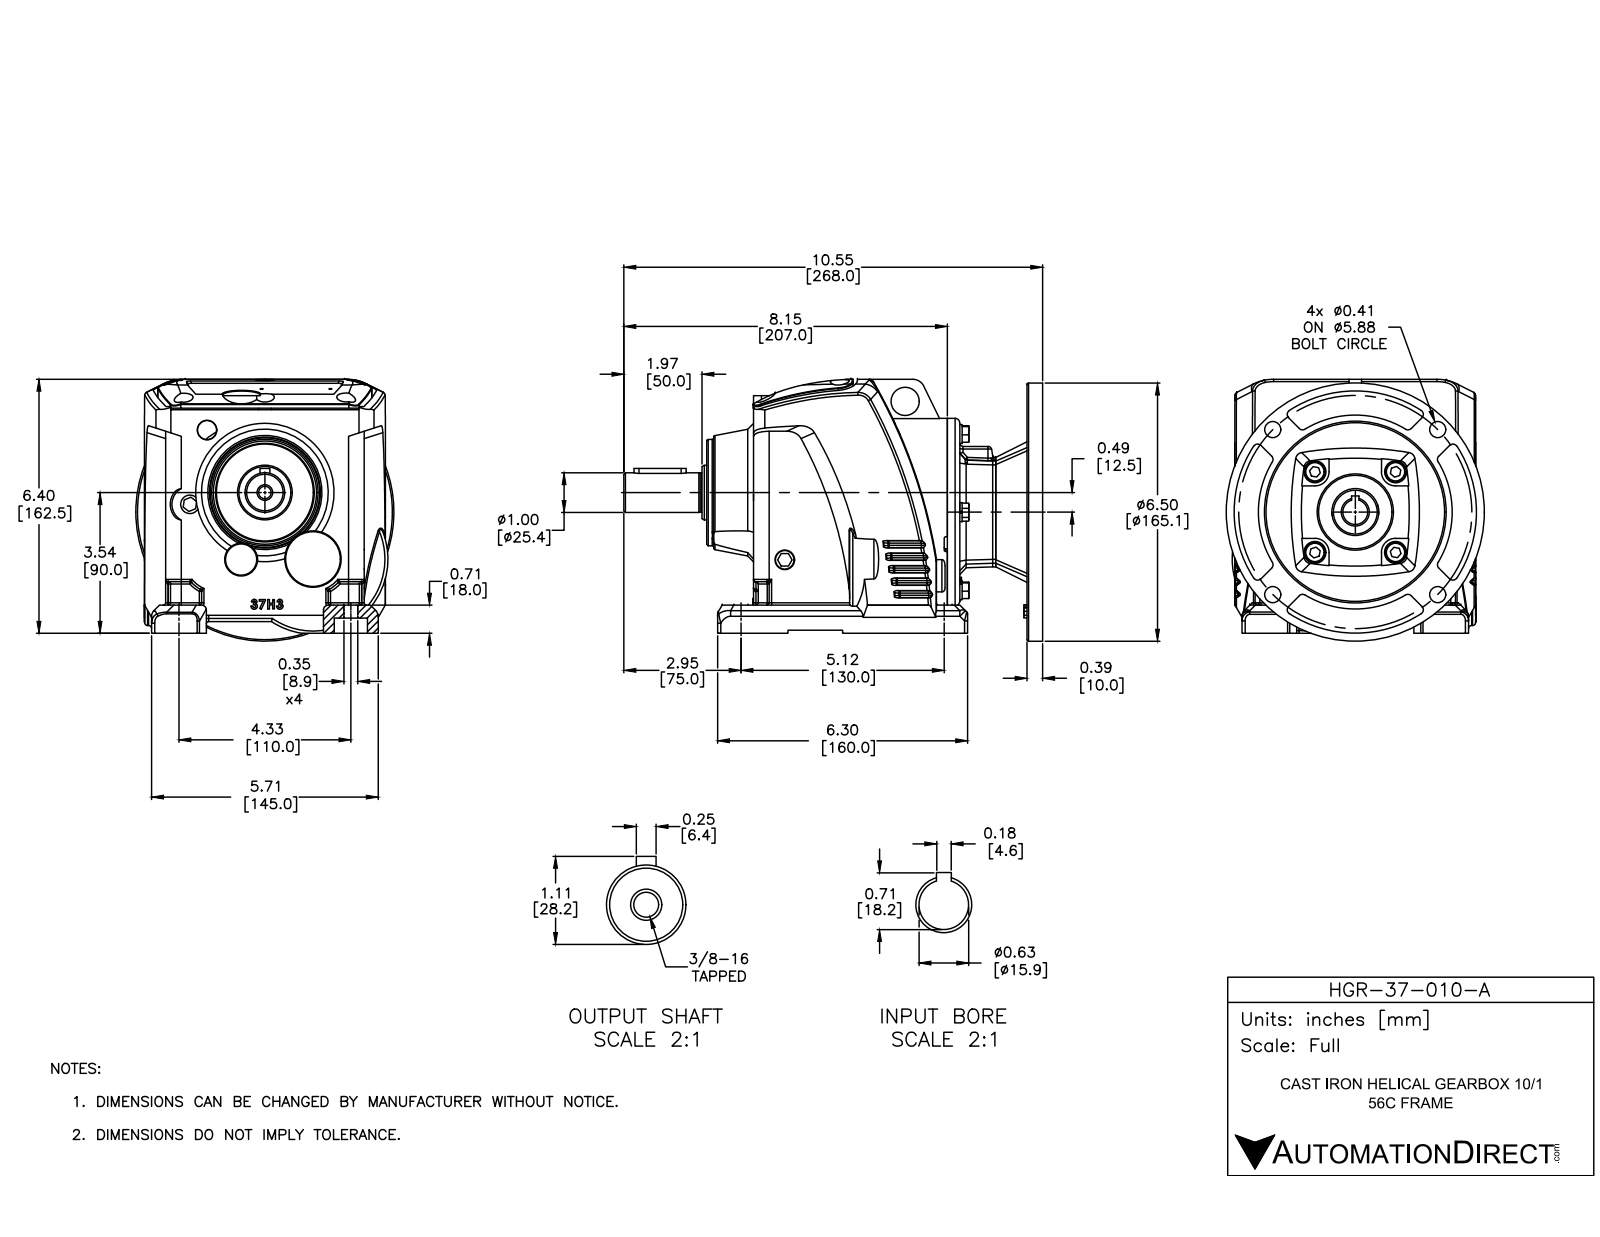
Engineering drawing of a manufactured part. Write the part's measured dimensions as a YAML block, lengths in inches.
part_name: "HGR-37-010-A"
step_written_by: "SolidWorks 2015 (AUTOMOTIVE_DESIGN)"
units: inches
bodies: {solids: 4, faces: 1036, planar: 343, cylindrical: 277, other: 416}
overall_size: [10.551, 6.596, 6.5]
volume: 169.7
surface_area: 383.8
round_holes:
  - {diameter: 0.472, count: 6}
  - {diameter: 0.406, count: 4}
  - {diameter: 0.55, count: 4}
  - {diameter: 0.276, count: 3}
  - {diameter: 0.079, count: 2}
  - {diameter: 0.354, count: 2}
  - {diameter: 0.394, count: 2}
  - {diameter: 0.313, count: 1}
  - {diameter: 0.625, count: 1}
  - {diameter: 0.709, count: 1}
  - {diameter: 0.945, count: 1}
  - {diameter: 1.181, count: 1}
round_bosses_or_shafts:
  - {diameter: 0.512, count: 4}
  - {diameter: 0.48, count: 4}
  - {diameter: 0.315, count: 4}
  - {diameter: 1.378, count: 2}
  - {diameter: 0.472, count: 2}
  - {diameter: 6.5, count: 1}
  - {diameter: 4.724, count: 1}
  - {diameter: 2.677, count: 1}
partial_cylinders:
  - {radius: 0.059, count: 43}
  - {radius: 0.118, count: 21}
  - {radius: 0.079, count: 18}
  - {radius: 0.197, count: 8}
  - {radius: 0.354, count: 6}
  - {radius: 0.394, count: 6}
  - {radius: 0.315, count: 5}
  - {radius: 0.276, count: 4}
face_to_face_distances: [7.126, 0.236, 0.276, 0.394, 6.89, 1.102, 4.331, 0.157, 2.087, 0.079]
hole_center_spacings: [3.27, 1.437, 1.5, 2.032, 2.937, 4.154, 4.374, 1.143]
